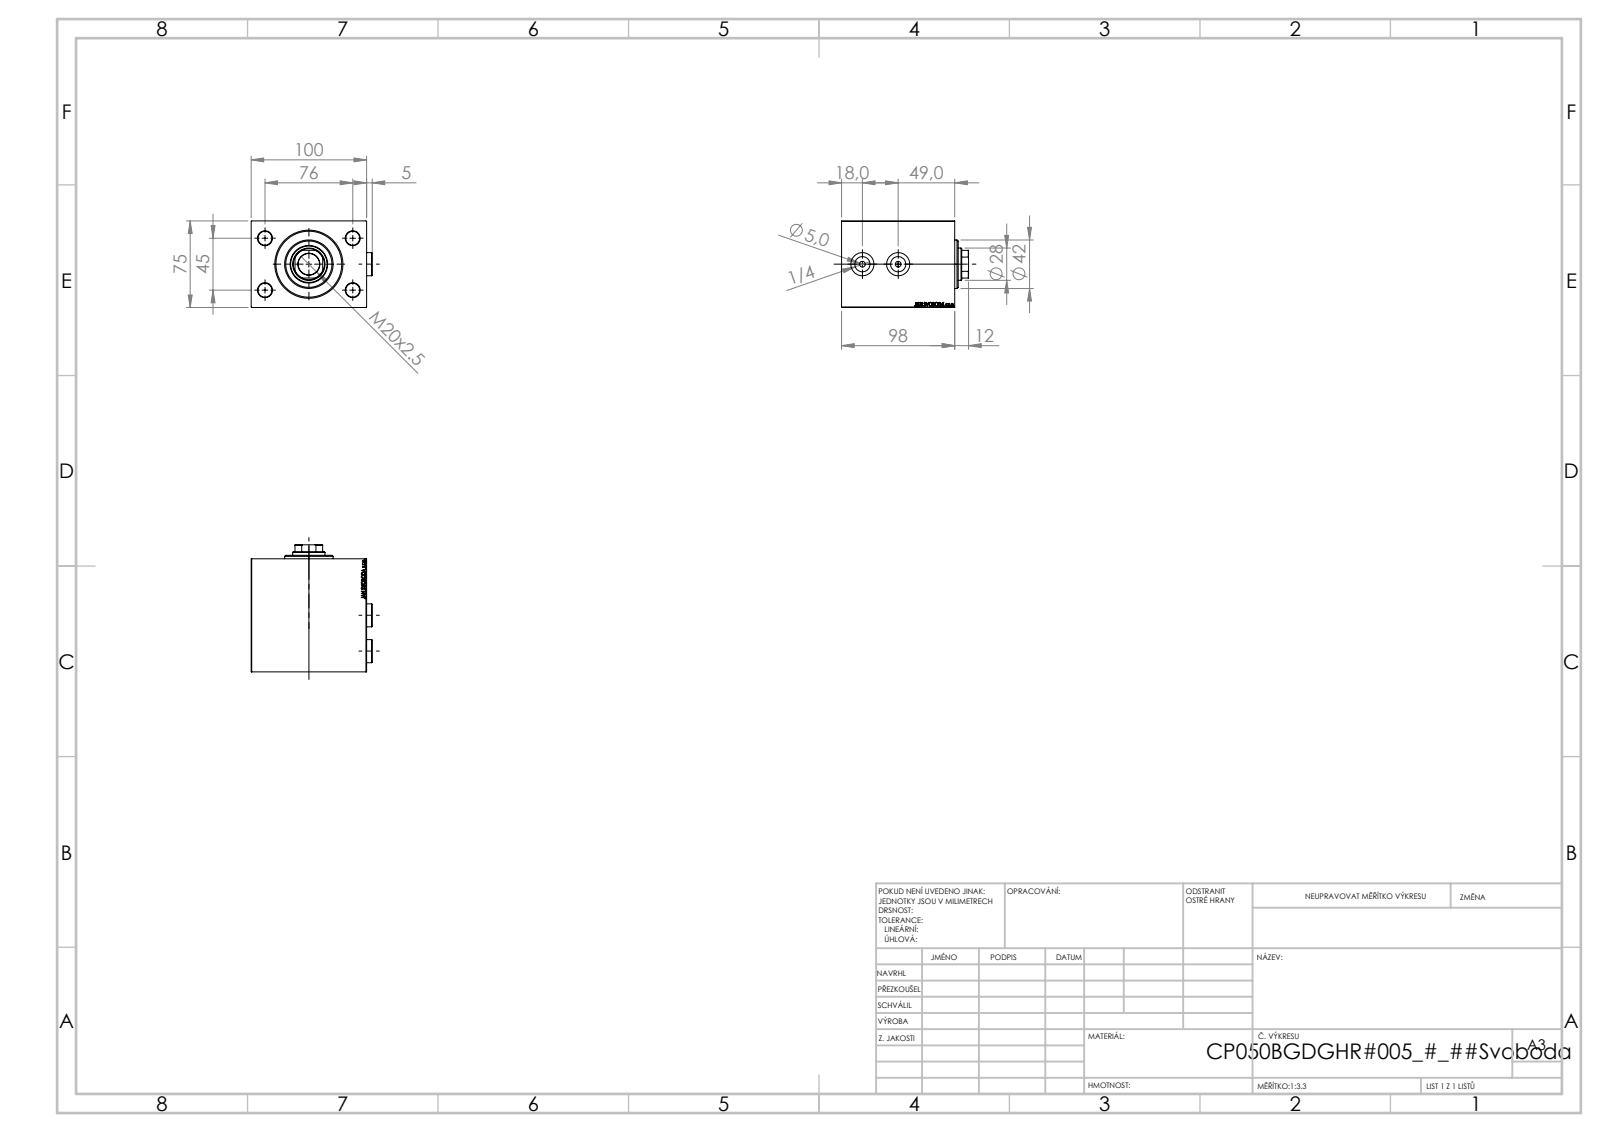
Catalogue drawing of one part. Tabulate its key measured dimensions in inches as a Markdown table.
| quantity | value |
| --- | --- |
| part name | V450CP_VC_B; PLUG; V450CP_B; V450CP_B_VCP |
| STEP written by | SolidWorks 2019 (CONFIG_CONTROL_DESIGN) |
| units | inches |
| bodies | 5 solids, 959 faces (441 planar, 84 cylindrical, 434 other) |
| overall size | 4.331 × 4.13 × 2.953 |
| volume | 42.94 in³ |
| surface area | 165.8 in² |
| round holes (diameter × count) | 0.472 × 4, 0.157 × 2, 0.197 × 2, 0.383 × 2, 0.518 × 2, 0.591 × 2, 0.787 × 2, 0.728 × 1, 1.102 × 1, 1.24 × 1, 1.28 × 1, 1.969 × 1 |
| round bosses / shafts (diameter × count) | 1.654 × 1 |
| partial cylindrical surfaces (radius × count) | 0.531 × 1 |
| main face-to-face distances | 2.953, 3.937, 3.858, 1.929, 0.551, 3.307, 0.197, 1.732, 1.378, 2.126 |
| hole center spacings | 1.739, 1.772, 2.992, 3.477, 1.22, 1.675 |
